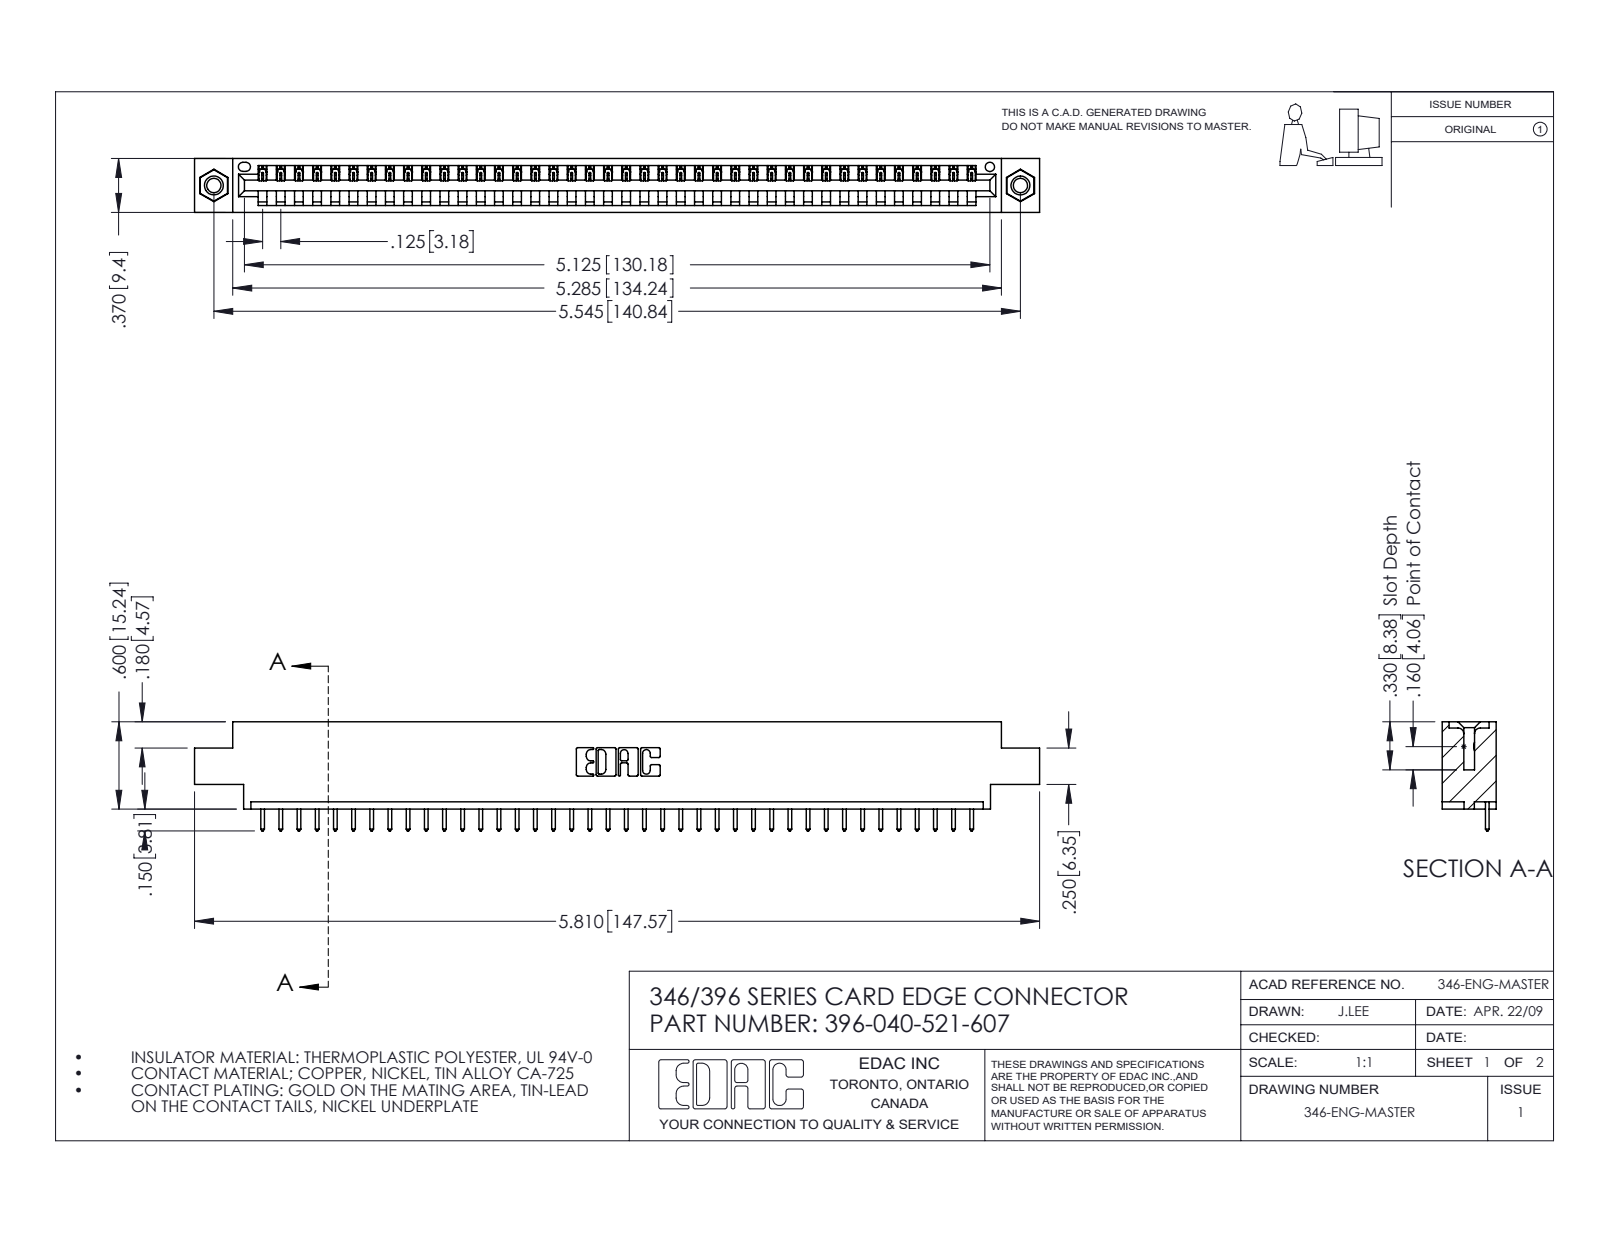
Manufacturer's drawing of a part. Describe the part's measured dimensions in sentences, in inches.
The part is named "396-040-521-607; 346 Part_0.170 Offset - 0.156 Dia-TI; 345-292-001_345-293-121; 345-250-001_345-250-005-103". Its 3-D file was written by "SolidWorks 2016 (CONFIG_CONTROL_DESIGN)". It is 43 solids with 2506 faces: 1712 planar, 778 cylindrical and 16 other. Overall it measures 5.81 by 0.75 by 0.37 inches. Its volume is 0.844 cubic inches and its surface area 26.36 square inches. Round holes: 2 of diameter 0.098, 2 of diameter 0.125, 2 of diameter 0.156, 1 of diameter 0.064. Round bosses or shafts: 2 of diameter 0.155. Partial cylindrical surfaces (rounded edges, fillets, slot ends): 80 of radius 0.006, 80 of radius 0.01, 22 of radius 0.01, 6 of radius 0.007, 6 of radius 0.031, 3 of radius 0.026, 2 of radius 0.031, 2 of radius 0.04. The main face-to-face distances are 0.048, 0.322, 0.37, 0.25, 0.072, 0.298, 0.025, 0.222, 0.148, 0.1. The hole center spacings are 0.246, 5.336, 5.545.
